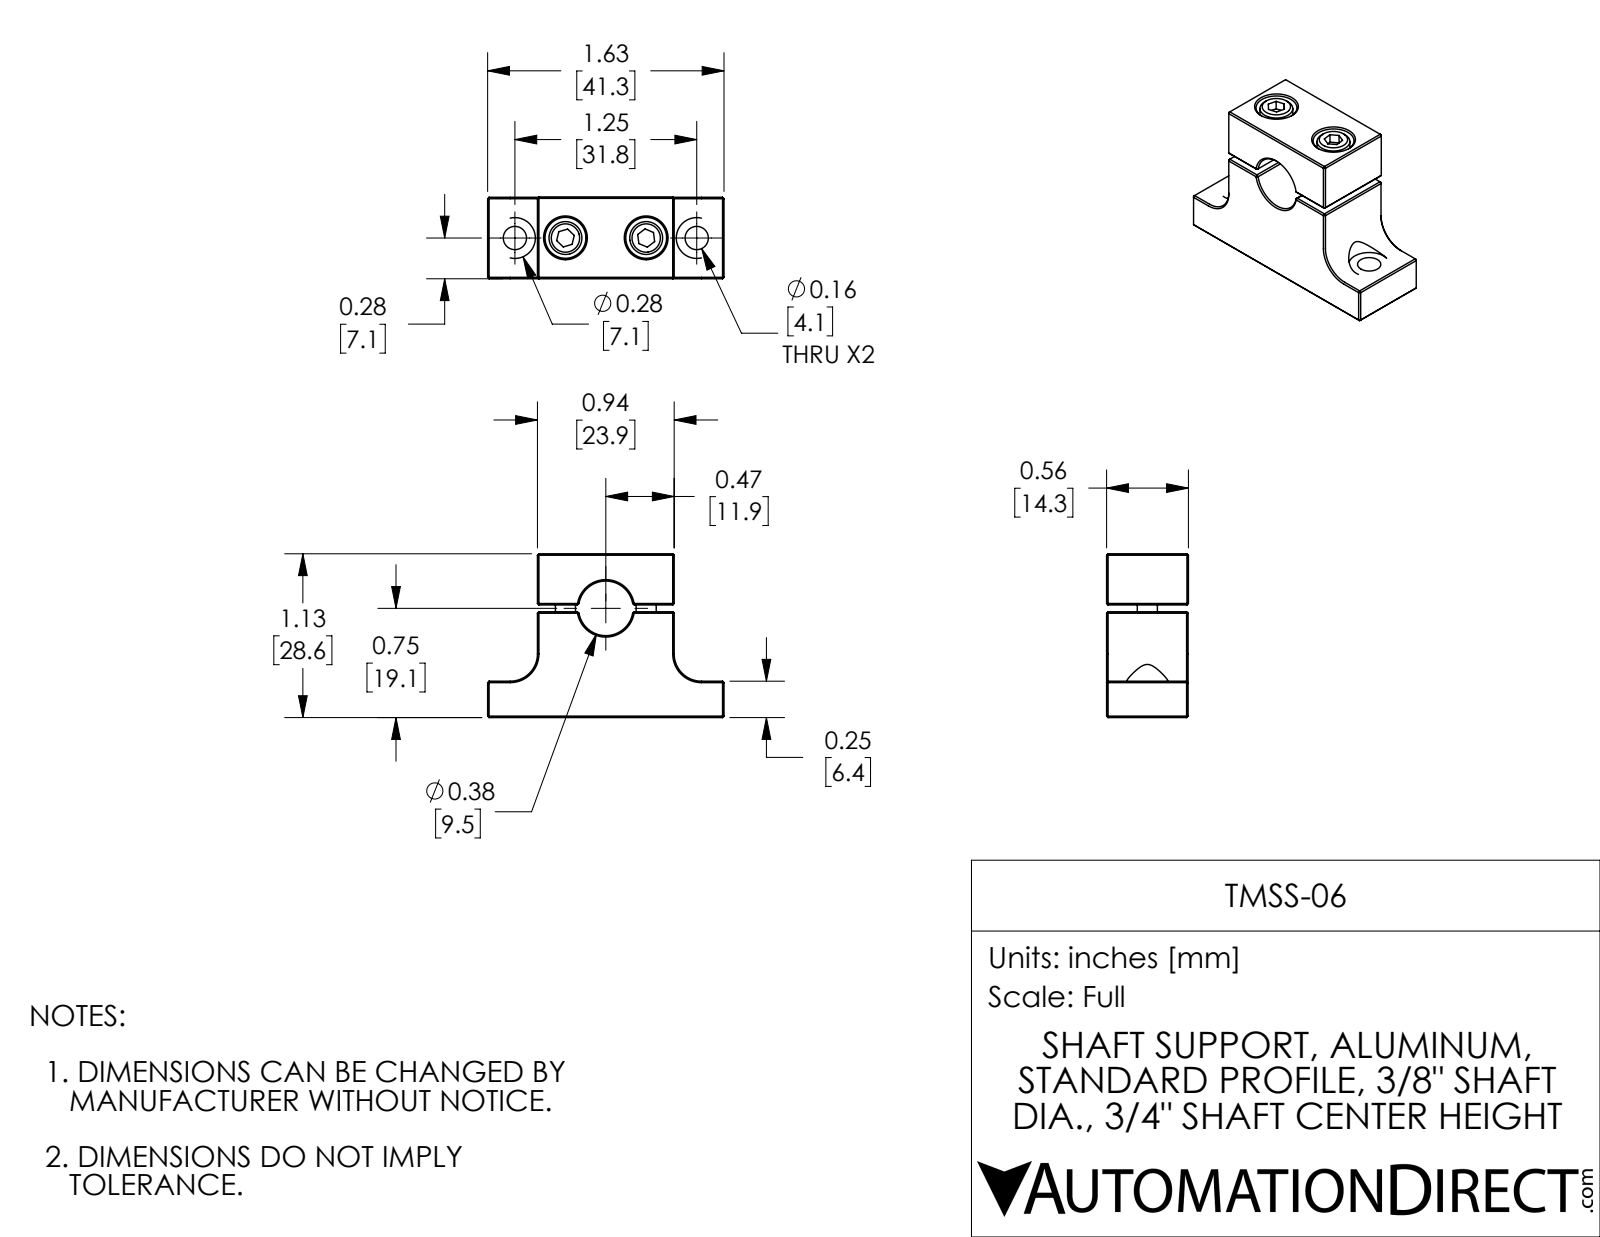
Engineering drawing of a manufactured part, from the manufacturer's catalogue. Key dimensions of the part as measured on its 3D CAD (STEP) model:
Part name (STEP PRODUCT): TMSS-06
STEP written by: SolidWorks 2017 (AUTOMOTIVE_DESIGN)
Units: inches
Bodies: 4 solids, 169 faces (110 planar, 34 cylindrical, 25 other)
Overall size (bounding box): 1.625 × 1.126 × 0.563
Volume: 0.595 in³ · Surface area: 8.084 in²
Round holes (diameter × count): ⌀0.104 ×2, ⌀0.15 ×2, ⌀0.16 ×2, ⌀0.281 ×2
Round bosses / shafts (diameter × count): ⌀0.226 ×2, ⌀0.138 ×2
Partial cylindrical surfaces — rounded edges, fillets, slot ends (radius × count): R0.187 ×3, R0.141 ×2, R0.188 ×1
Main face-to-face distances: 0.56, 1.125, 0.94, 0.727, 0.398, 0.563, 0.774, 0.047, 0.351, 0.343
Hole centre spacings: 0.348, 0.555, 0.903, 1.25
